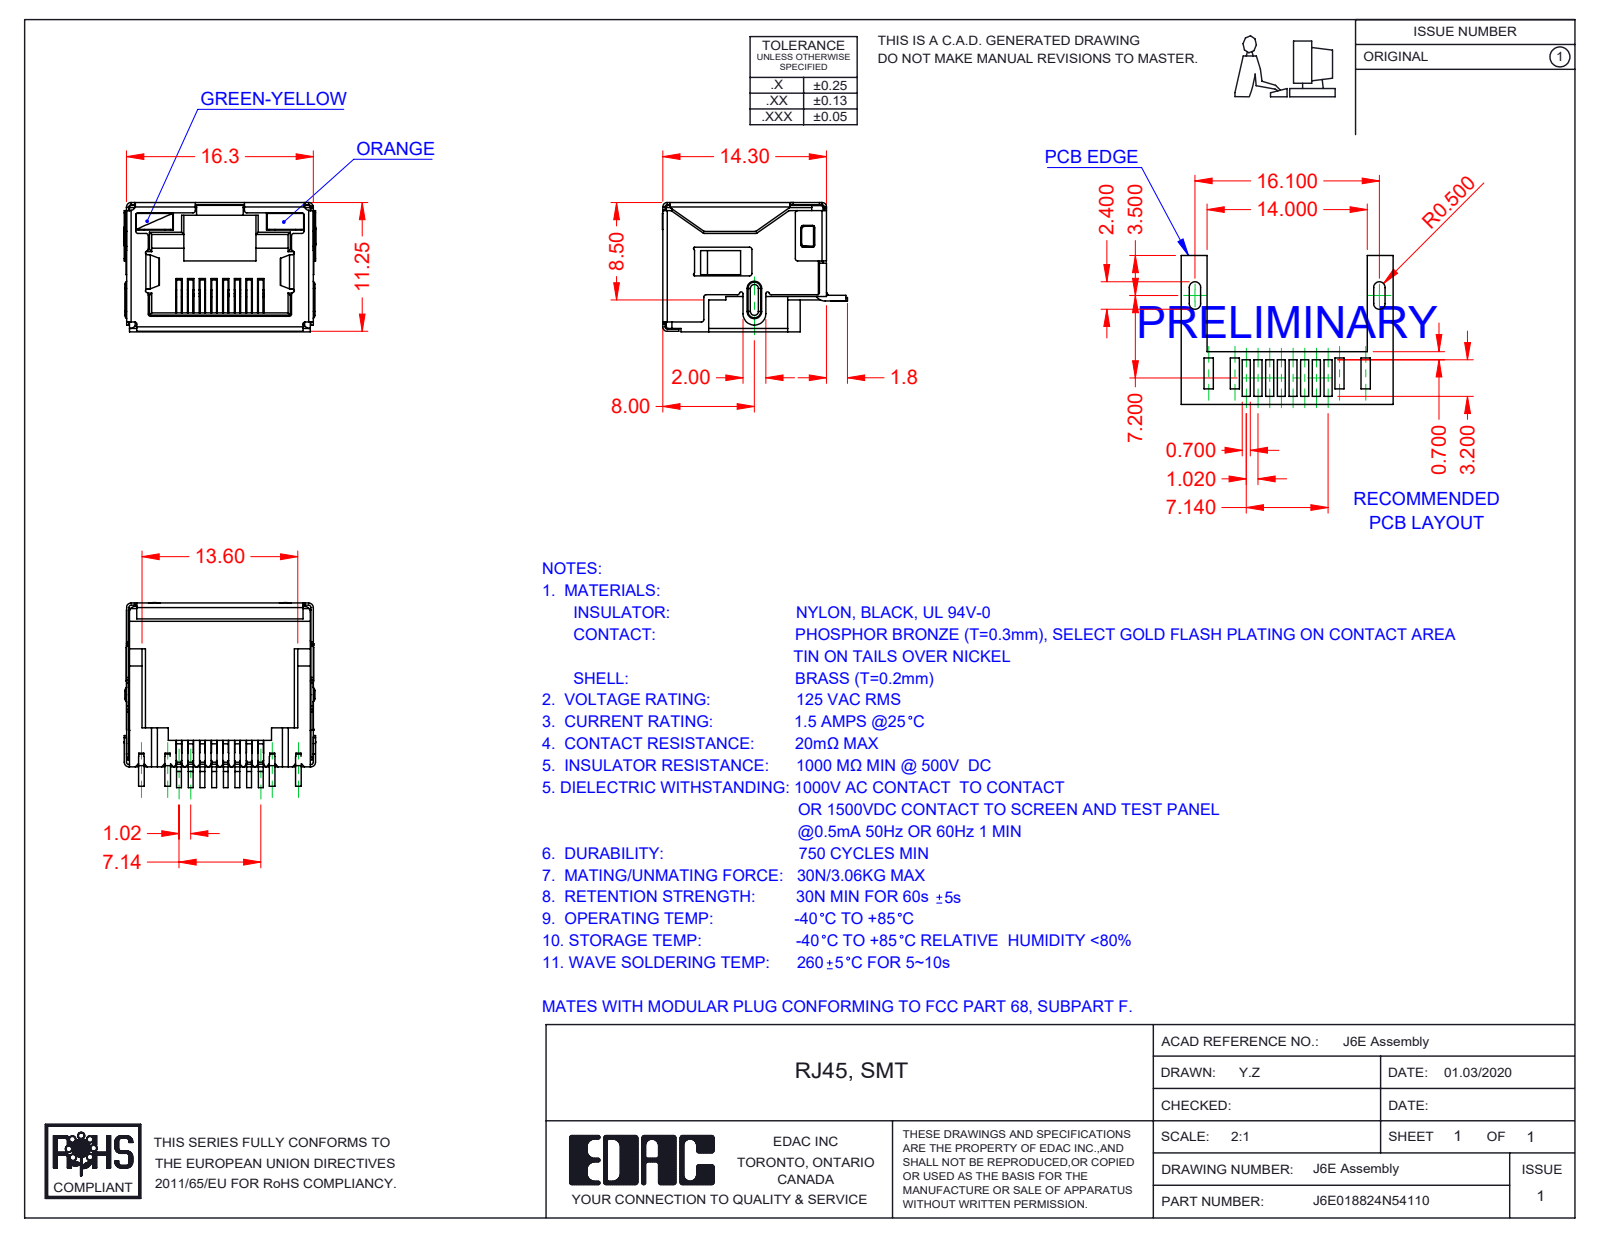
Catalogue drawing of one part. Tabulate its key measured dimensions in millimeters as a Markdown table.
| quantity | value |
| --- | --- |
| part name | 6E LED RH_4-Orange; 6E Insulator_LED; 6E Shield_LED; 6E Contacts (+2 more) |
| STEP written by | SolidWorks 2016 (CONFIG_CONTROL_DESIGN) |
| units | millimeters |
| bodies | 12 solids, 1498 faces (1099 planar, 349 cylindrical, 50 other) |
| overall size | 16.75 × 16.15 × 11.3 |
| volume | 1 109 mm³ |
| surface area | 4 045 mm² |
| partial cylindrical surfaces (radius × count) | 0.2 × 82, 0.25 × 17, 0.4 × 13, 0.5 × 13, 0.1 × 10, 0.15 × 7, 0.3 × 4, 1 × 3 |
| main face-to-face distances | 11.05, 16.05, 16.1, 15.85, 11.1, 11.3, 2.4, 0.7, 9.85, 0.49 |
